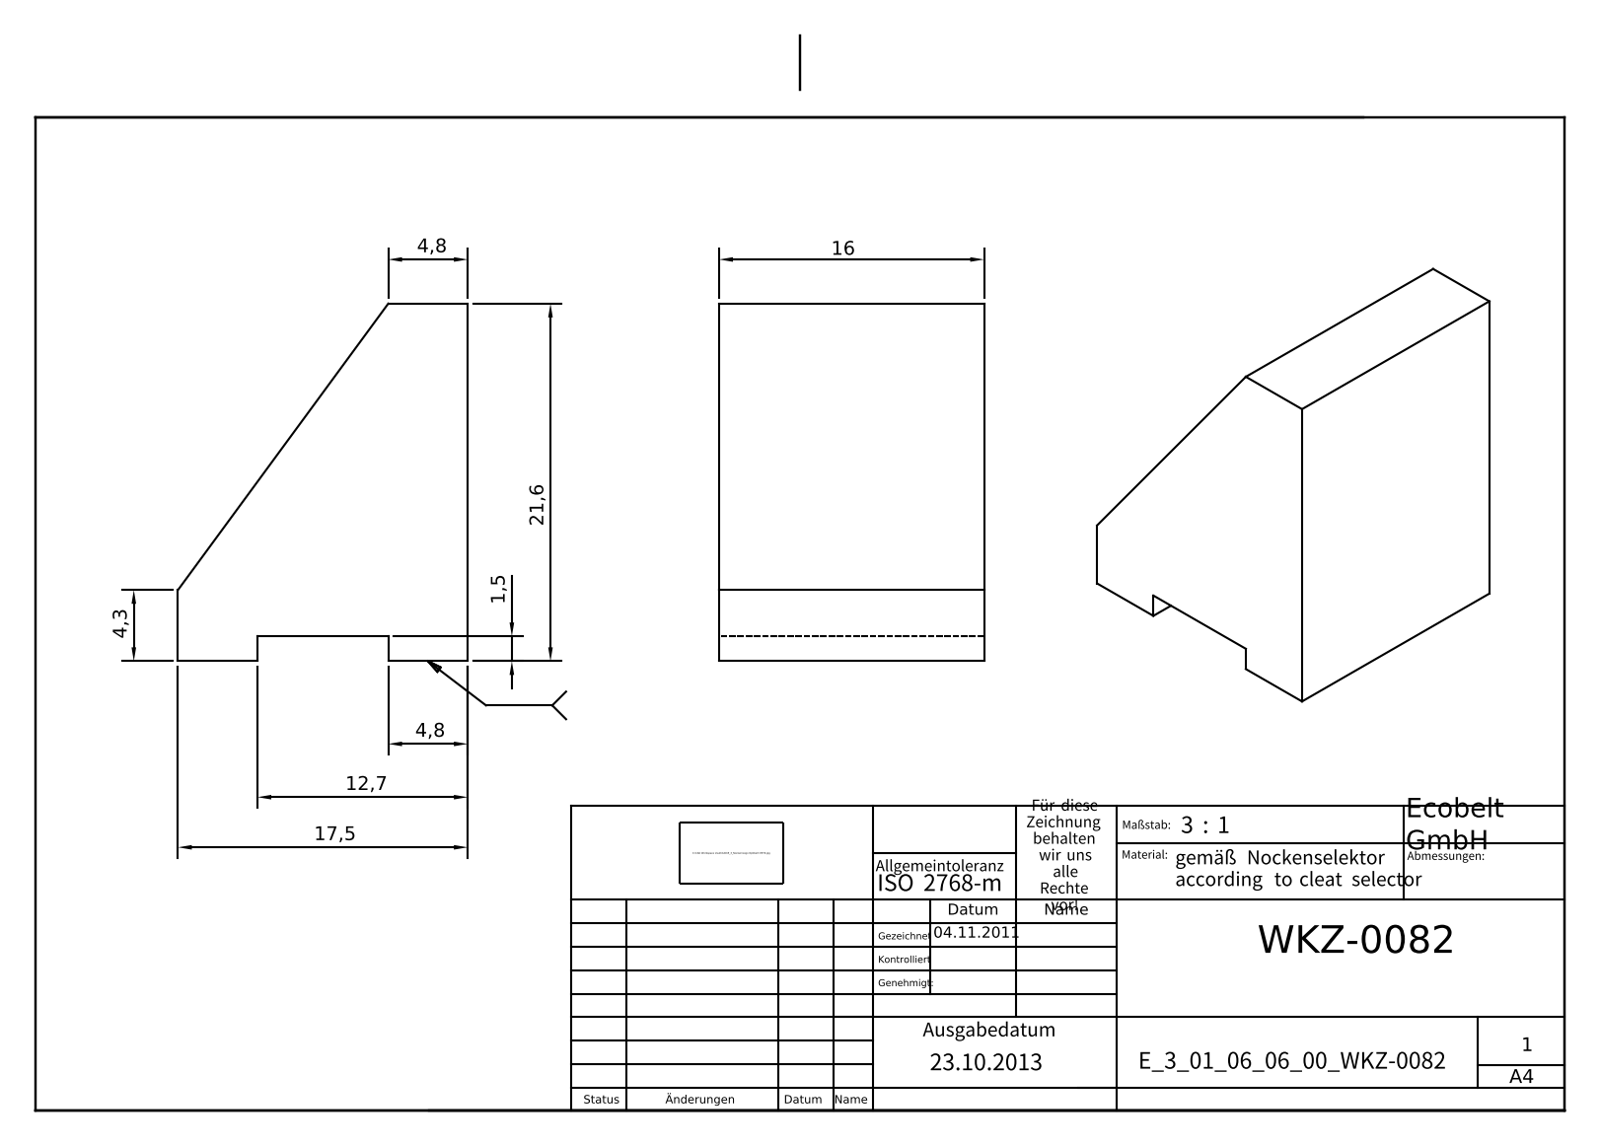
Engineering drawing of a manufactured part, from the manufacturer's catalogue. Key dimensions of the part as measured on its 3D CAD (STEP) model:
Part name (STEP PRODUCT): E_3_01_06_06_00_WKZ-0082
STEP written by: Autodesk Inventor 2025 (AUTOMOTIVE_DESIGN)
Units: millimetres
Bodies: 1 solid, 11 faces (11 planar, 0 cylindrical, 0 other)
Overall size (bounding box): 21.6 × 17.5 × 16
Volume: 4 101 mm³ · Surface area: 1 675 mm²
Main face-to-face distances: 16, 1.5, 21.6, 20.1, 17.5, 4.8, 12.7, 7.9
